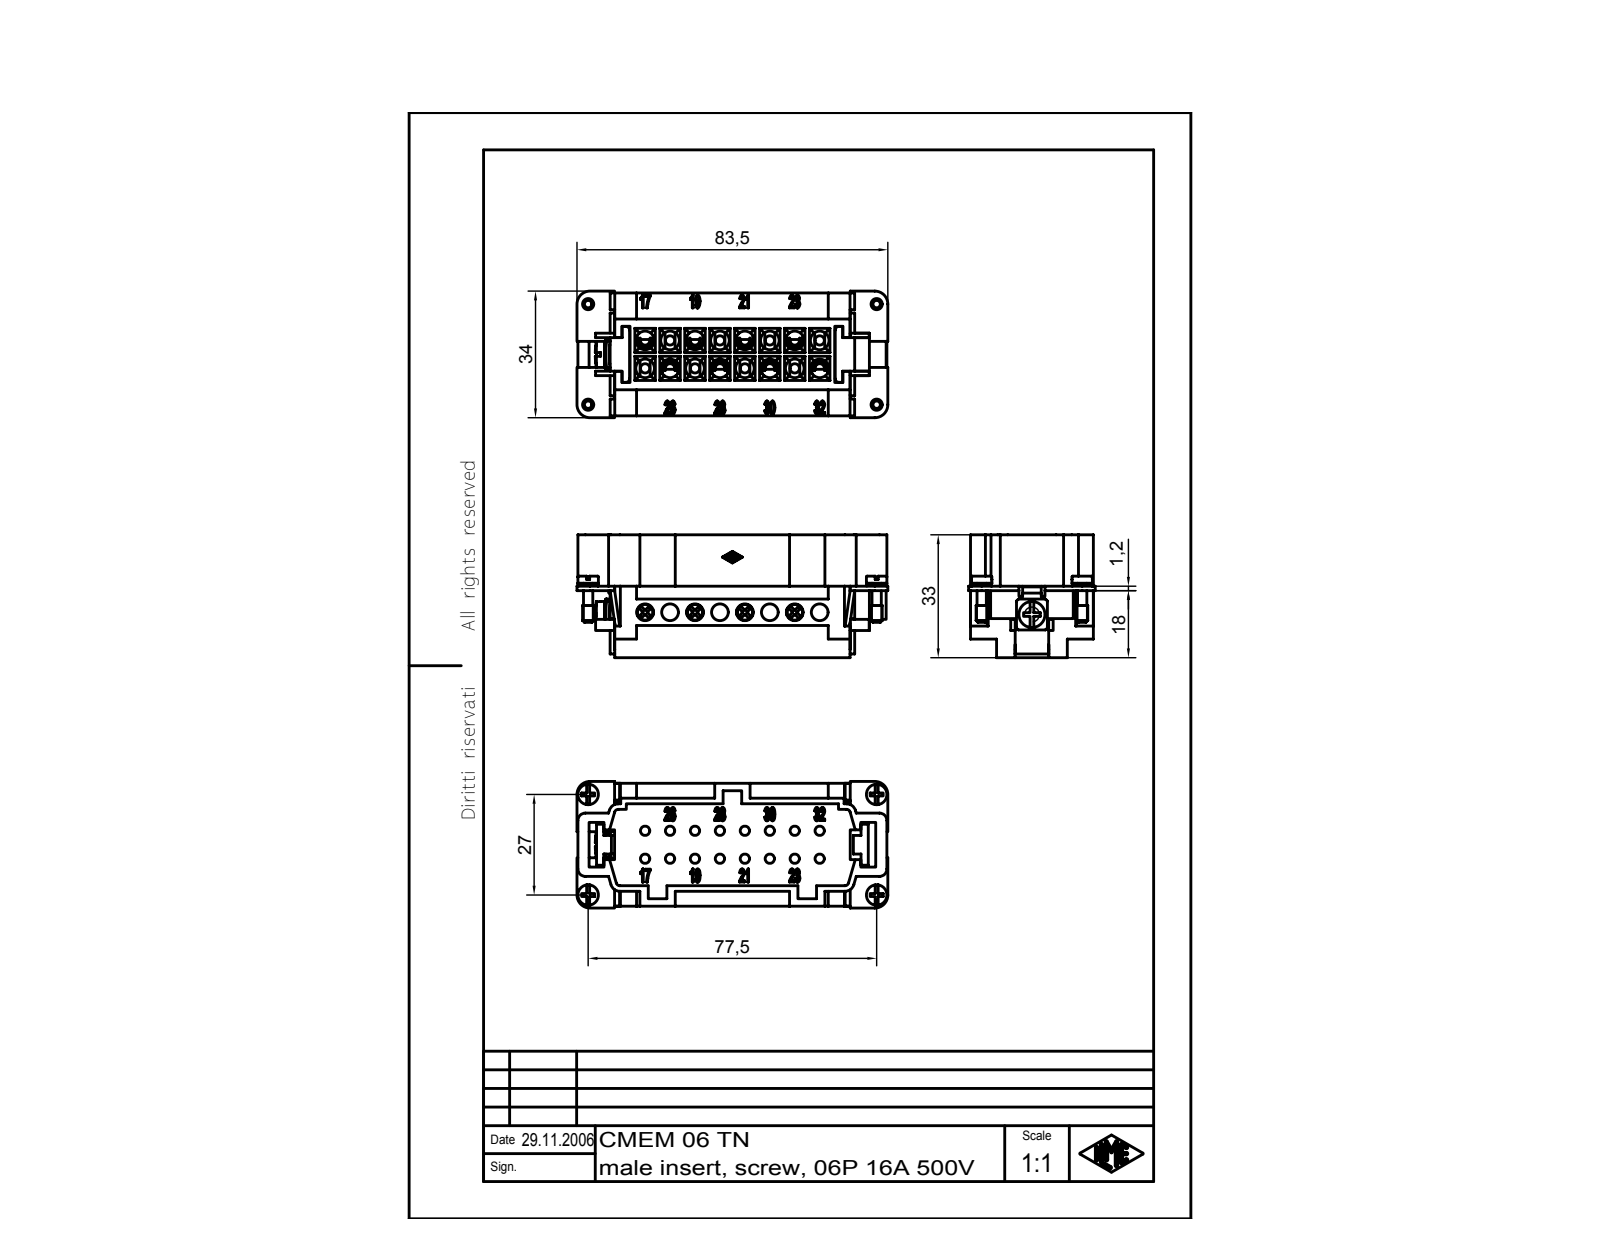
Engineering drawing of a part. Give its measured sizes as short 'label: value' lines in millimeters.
name: CMEM 06 TN
written by: Autodesk Inventor 7 (AUTOMOTIVE_DESIGN)
unit: mm
bodies: 9 solids, 1575 faces (720 planar, 229 cylindrical, 626 other)
size: 83.5 × 34 × 33
volume: 33 062 mm³; area: 29 984 mm²
holes: 8× ⌀2.5, 8× ⌀3, 8× ⌀4.5, 8× ⌀5, 2× ⌀2.55
bosses: 8× ⌀4.2, 6× ⌀2.5, 2× ⌀5.5, 2× ⌀5.3, 2× ⌀3, 1× ⌀7
rounds: 14× R0.1, 8× R2.1, 6× R1, 6× R2, 4× R2.5, 2× R3.5, 1× R1.62, 1× R5.5
face distances: 1.5, 22, 3, 20.5, 4, 5.5, 23.5, 29, 7, 1
hole spacings: 6.7, 13.4, 20.1, 10.06, 15.36, 26.8, 21.45, 33.5
